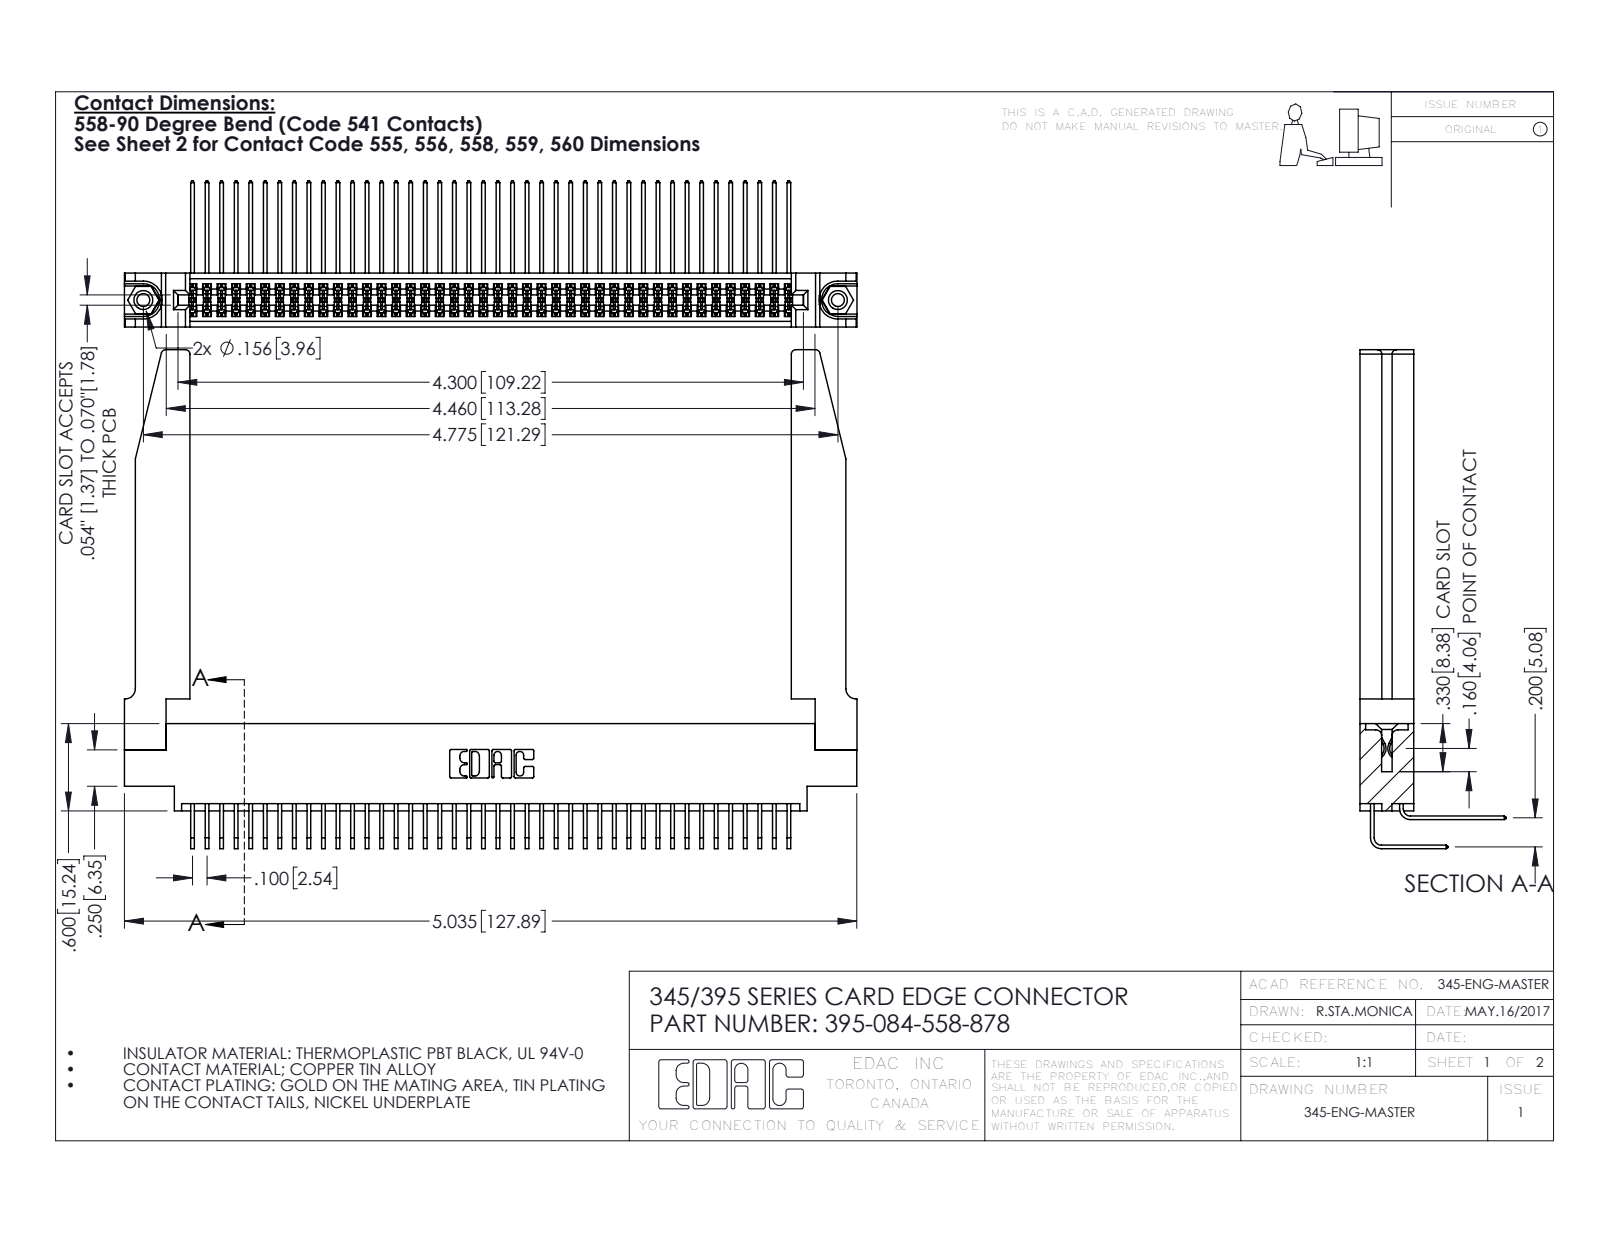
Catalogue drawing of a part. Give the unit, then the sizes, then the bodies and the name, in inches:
Units: inches
Overall size (bounding box): 5.036 × 3.429 × 1.005
Round holes (diameter × count): ⌀0.089 ×2, ⌀0.125 ×2, ⌀0.156 ×2, ⌀0.064 ×1
Round bosses / shafts (diameter × count): ⌀0.155 ×2
Partial cylindrical surfaces — rounded edges, fillets, slot ends (radius × count): R0.006 ×127, R0.01 ×22, R0.03 ×8, R0.007 ×6, R0.031 ×6, R0.026 ×3, R0.014 ×2, R0.019 ×2
Main face-to-face distances: 0.37, 0.072, 0.298, 0.2, 0.098, 0.272, 0.025, 0.225, 0.175, 0.148
Hole centre spacings: 0.27, 4.539, 4.775
Volume: 1.255 in³ · Surface area: 43.67 in²
Bodies: 89 solids, 4732 faces (3166 planar, 1514 cylindrical, 52 other)
Part name (STEP PRODUCT): 395-084-558-878; 345 Part_0.170 Offset - 0.156 Dia-TH; 345-292-001_558 Tail - 2; 345-250-001_345-250-001-102 (+2 more)
STEP written by: SolidWorks 2016 (CONFIG_CONTROL_DESIGN)
